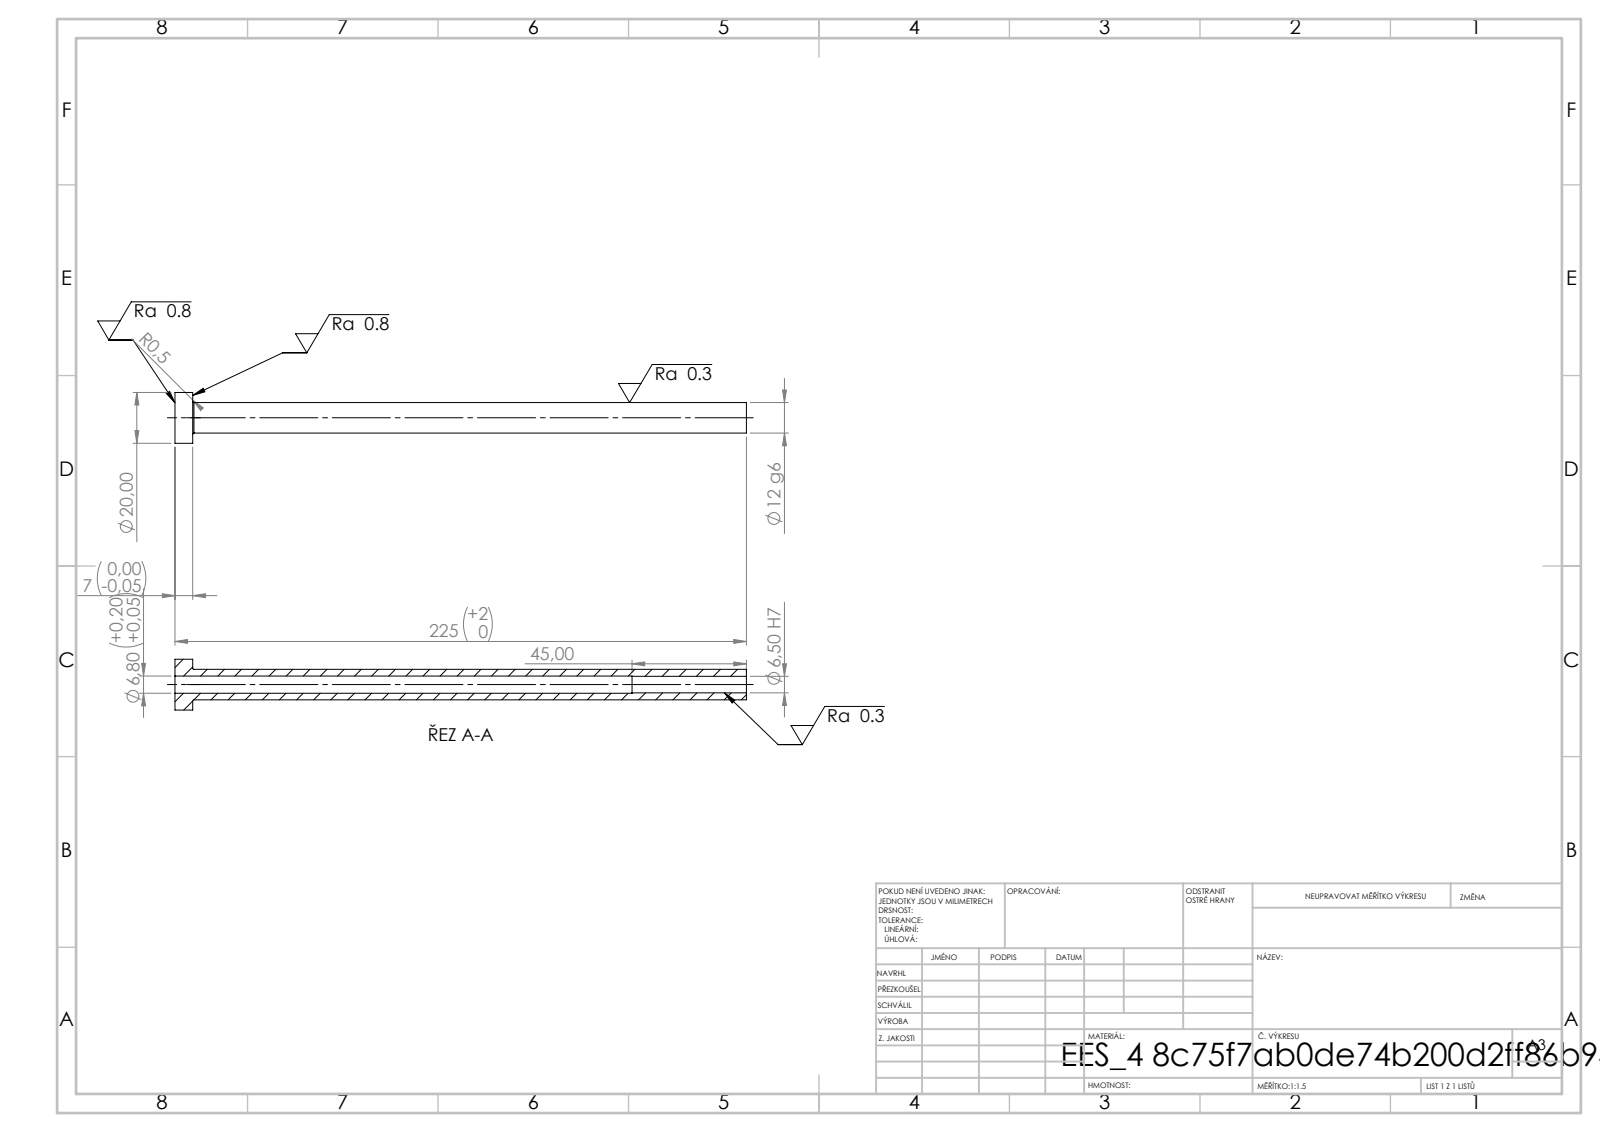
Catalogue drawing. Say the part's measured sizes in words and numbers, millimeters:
Its 3-D file was written by "SolidWorks 2019 (CONFIG_CONTROL_DESIGN)". It is 1 solid with 14 faces: 4 planar, 8 cylindrical and 2 other. Overall it measures 225 by 20 by 20 millimeters. Its volume is 18 826 cubic millimeters and its surface area 13 976 square millimeters. Round holes: 1 of diameter 6.5, 1 of diameter 6.8. Round bosses or shafts: 1 of diameter 20, 1 of diameter 12. The main face-to-face distances are 7, 225, 218, 180, 173, 45.
